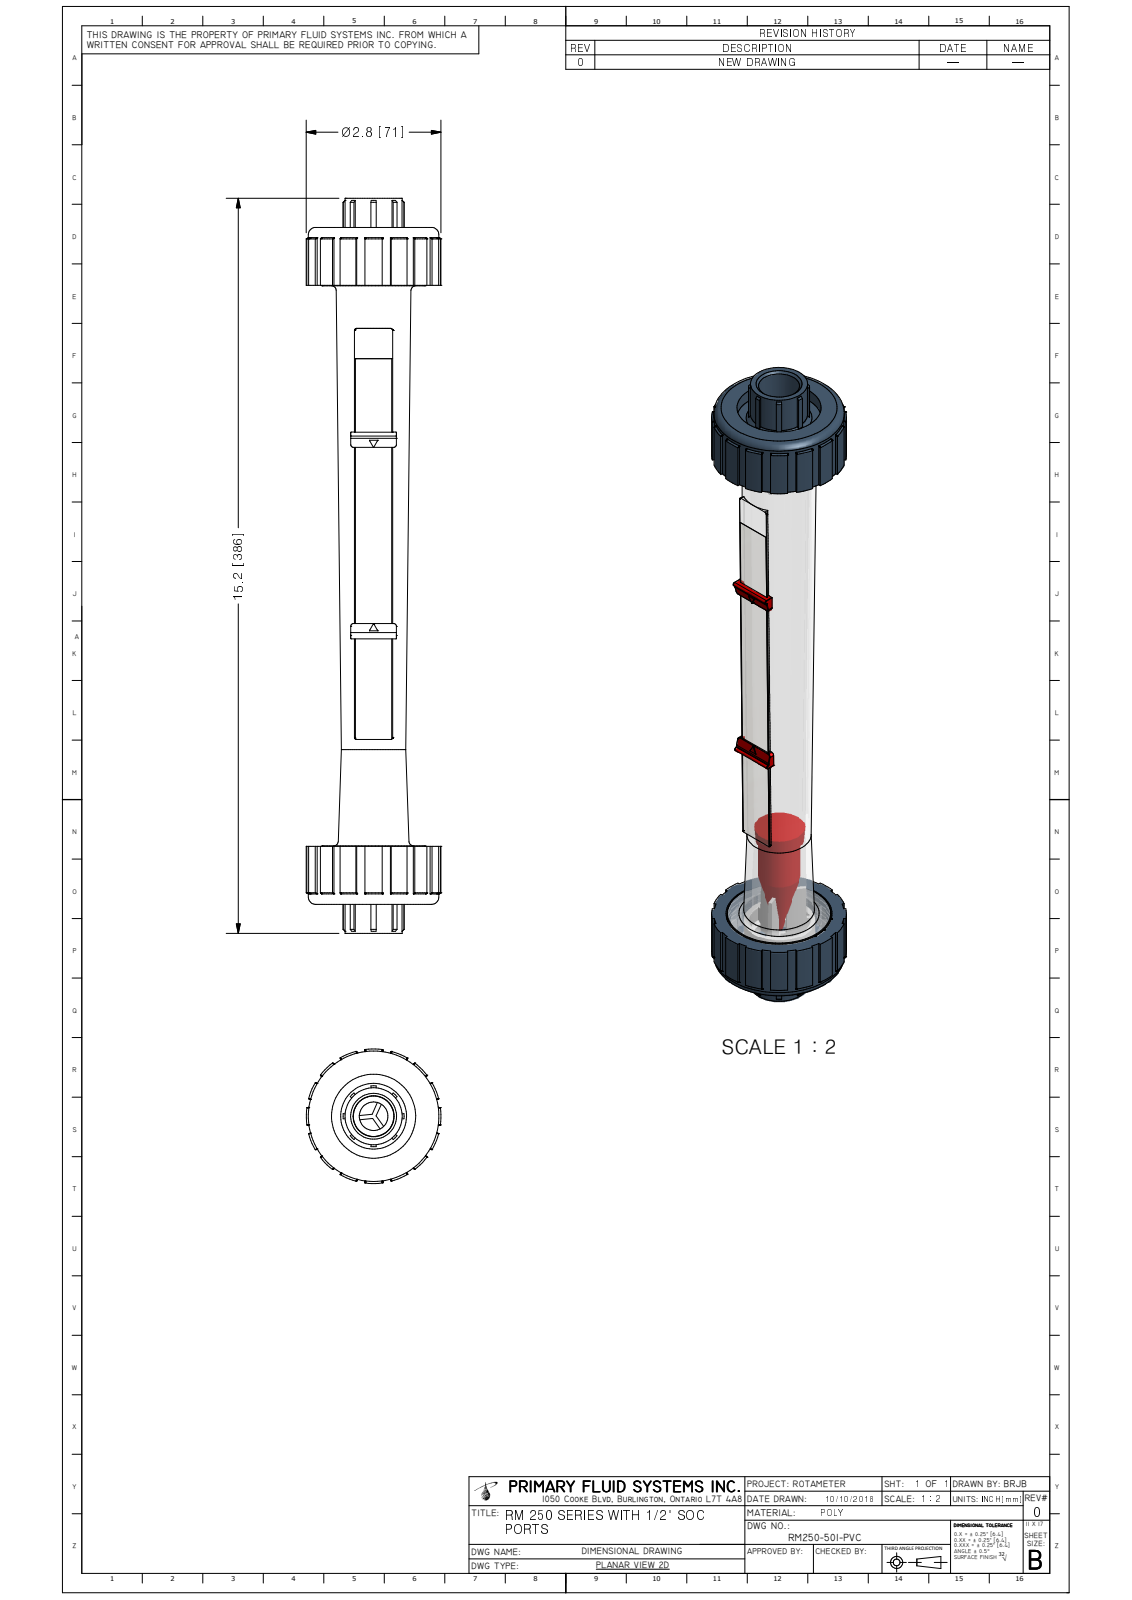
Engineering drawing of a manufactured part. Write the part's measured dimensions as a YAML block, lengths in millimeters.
part_name: "RM250-50I-PVC_R0"
step_written_by: "Autodesk Inventor 2009 (AUTOMOTIVE_DESIGN)"
units: millimeters
bodies: {solids: 1, faces: 587, planar: 230, cylindrical: 140, other: 217}
overall_size: [386.1, 70.7, 70.7]
volume: 526000
surface_area: 107100
round_holes:
  - {diameter: 44.1, count: 1}
  - {diameter: 55.6, count: 1}
round_bosses_or_shafts:
  - {diameter: 68.5, count: 1}
  - {diameter: 54.7, count: 1}
  - {diameter: 51.6, count: 1}
  - {diameter: 37.7, count: 1}
  - {diameter: 30, count: 1}
partial_cylinders:
  - {radius: 0.2, count: 18}
  - {radius: 0.3, count: 16}
  - {radius: 0.1, count: 10}
  - {radius: 0.2, count: 4}
  - {radius: 1.5, count: 4}
  - {radius: 0.2, count: 2}
  - {radius: 1, count: 2}
  - {radius: 1.1, count: 2}
face_to_face_distances: [30.4, 325.1, 30.7, 324.8, 294.4, 12.6, 342.8, 17.8, 312.4, 6.5]
